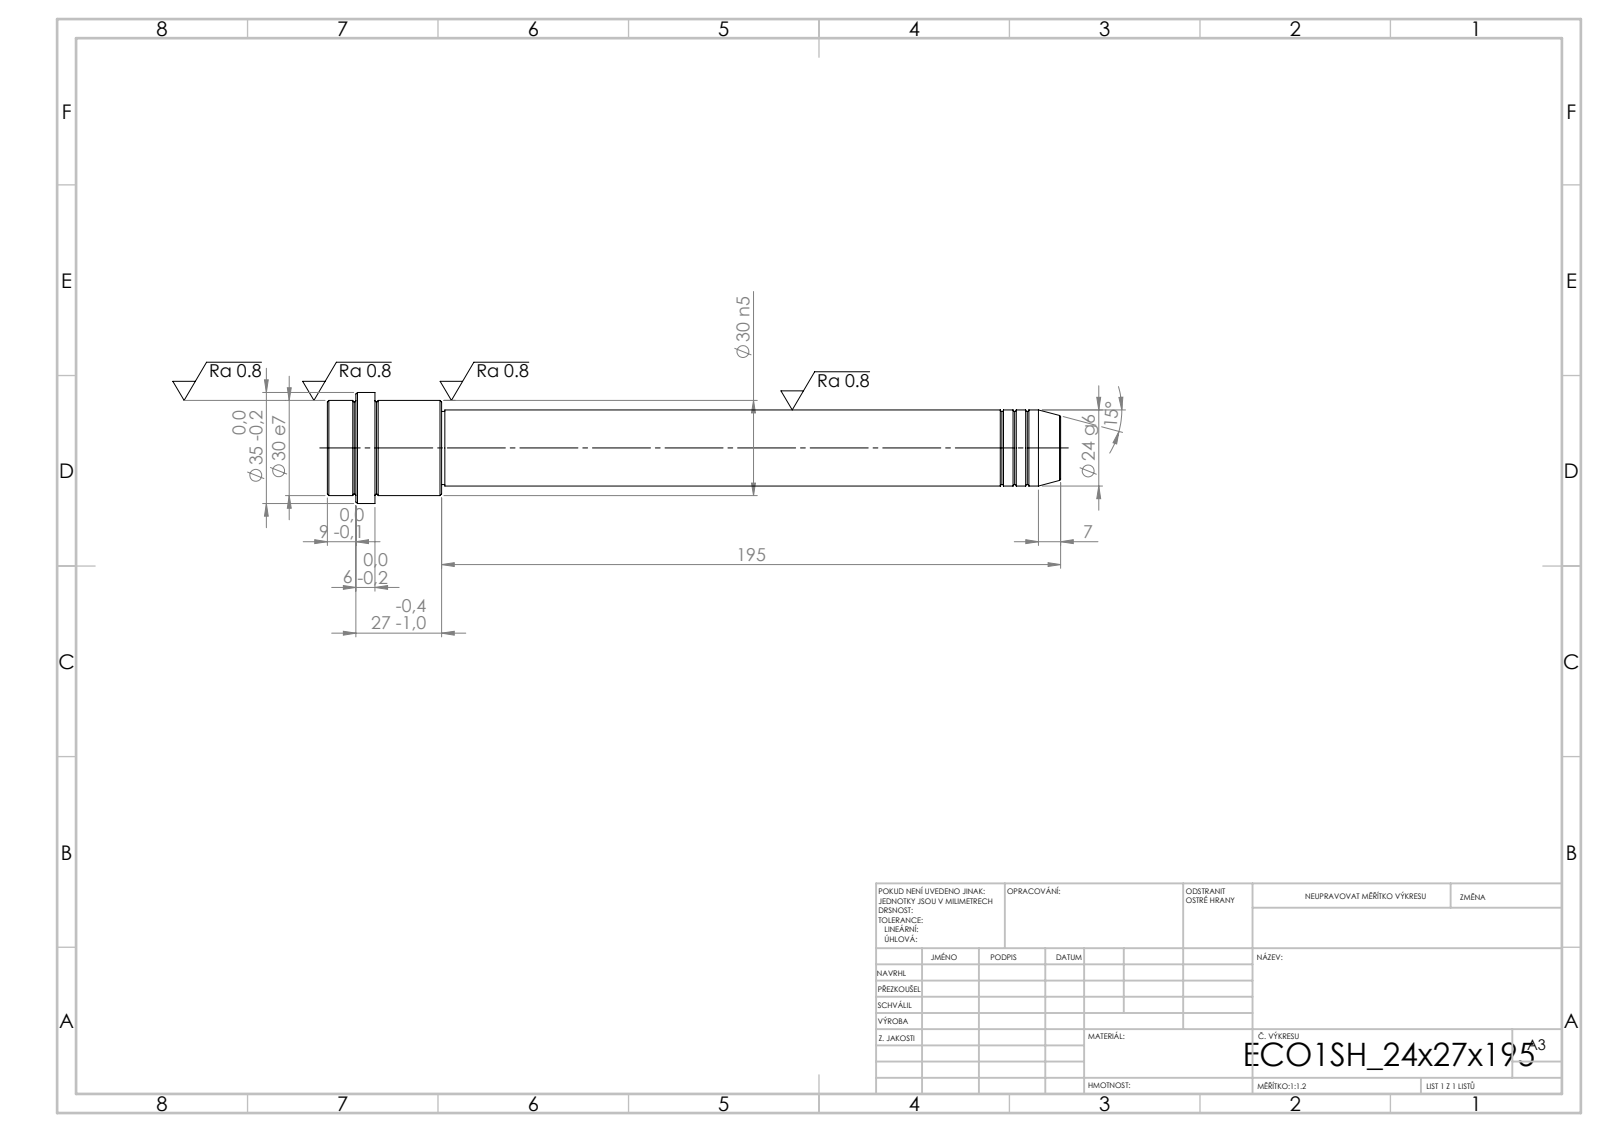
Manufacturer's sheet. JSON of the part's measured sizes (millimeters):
{"step_written_by": "SolidWorks 2019 (CONFIG_CONTROL_DESIGN)", "units": "millimeters", "bodies": {"solids": 1, "faces": 52, "planar": 6, "cylindrical": 16, "other": 30}, "overall_size": [231, 35, 35], "volume_mm3": 114489, "surface_area_mm2": 20156, "round_bosses_or_shafts": [[35, 1], [30, 1], [24, 1], [23, 1]], "face_to_face_distances": [231, 216, 15, 195, 21, 36, 222, 27, 6, 9]}
